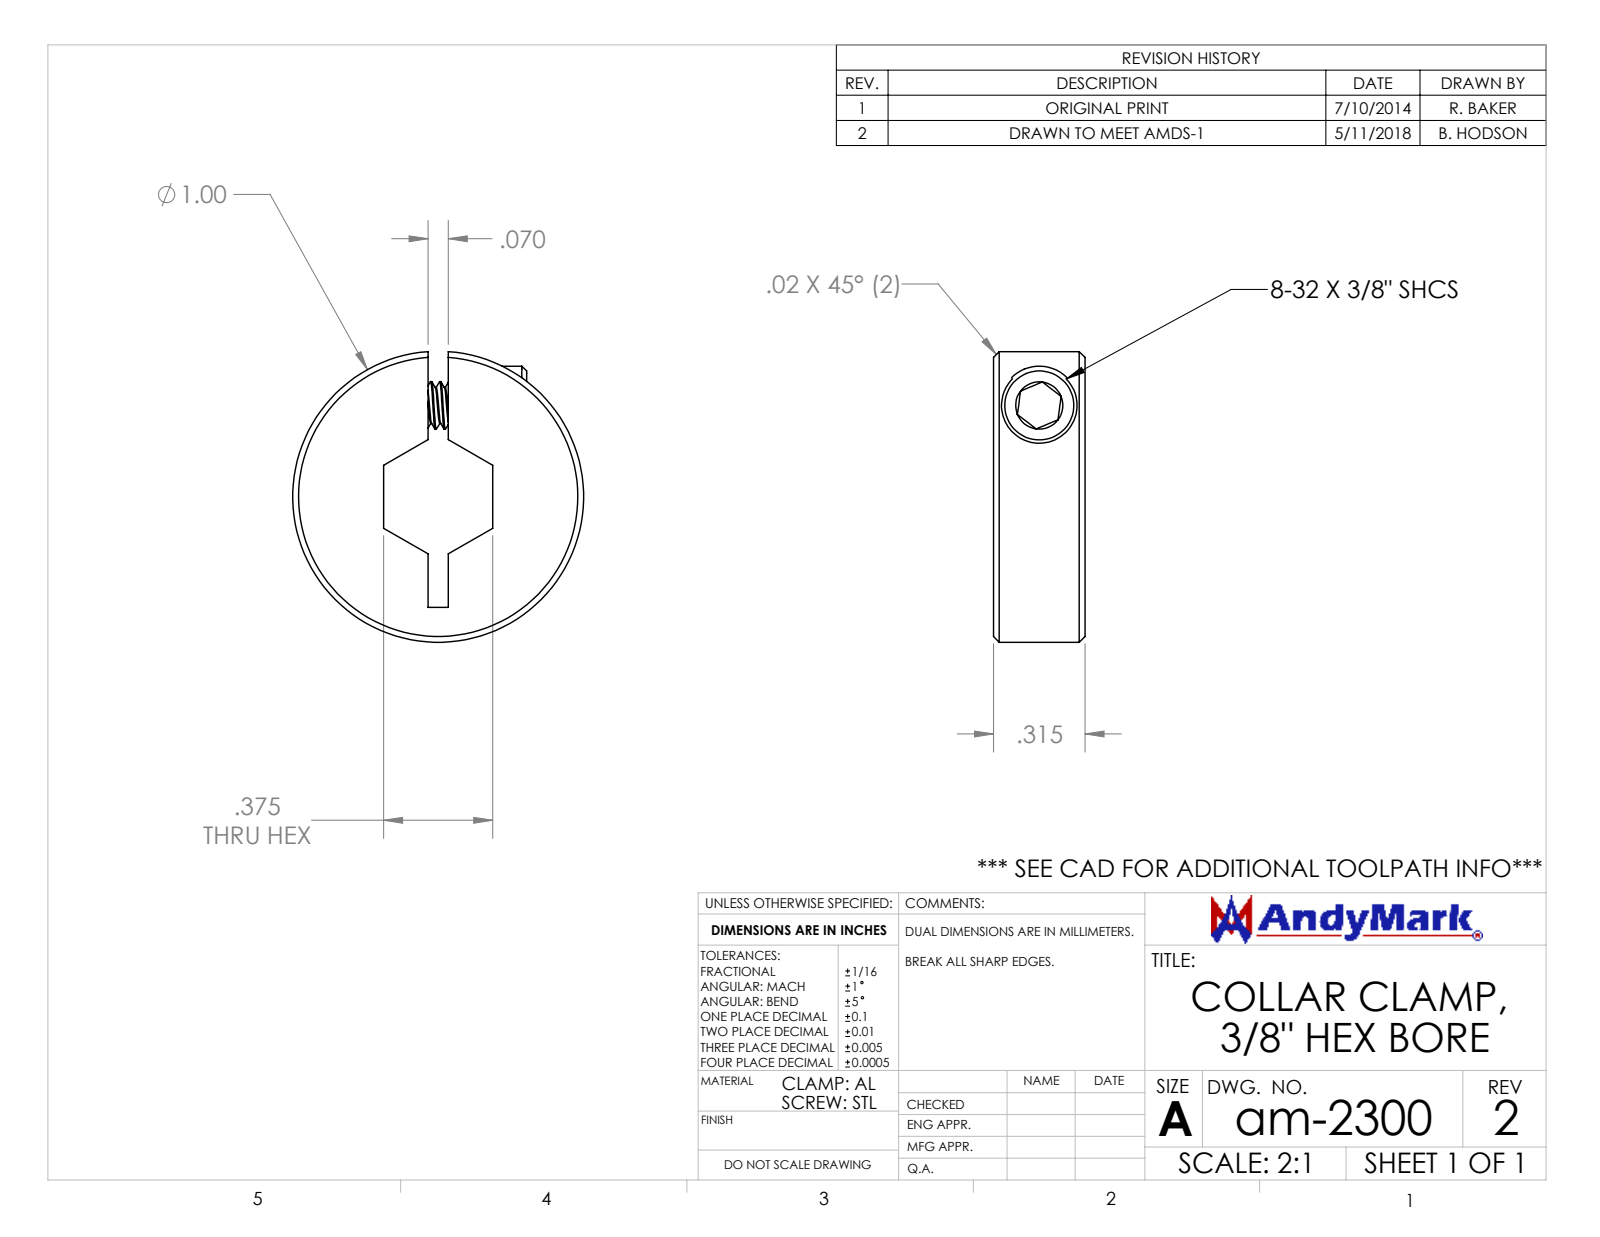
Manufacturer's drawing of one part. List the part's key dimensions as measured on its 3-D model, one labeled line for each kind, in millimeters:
Part name (STEP PRODUCT): am-2300 Collar Clamp, 0.375'''''''' Hex Bore, Aluminum REV2; am-2300 Clamp Only; am-2300 Screw Only_91251A192
STEP written by: SolidWorks 2017 (AUTOMOTIVE_DESIGN)
Units: millimetres
Bodies: 2 solids, 105 faces (24 planar, 60 cylindrical, 21 other)
Overall size (bounding box): 25.4 × 25.4 × 8
Volume: 3 100 mm³ · Surface area: 2 407 mm²
Round holes (diameter × count): ⌀6.6 ×1
Round bosses / shafts (diameter × count): ⌀25.4 ×1, ⌀6.9 ×1, ⌀4.2 ×1, ⌀3.1 ×1
Main face-to-face distances: 8, 9.5, 3.9, 5.6, 1.8, 8.3, 4.4, 2.7, 1.2, 3.6
